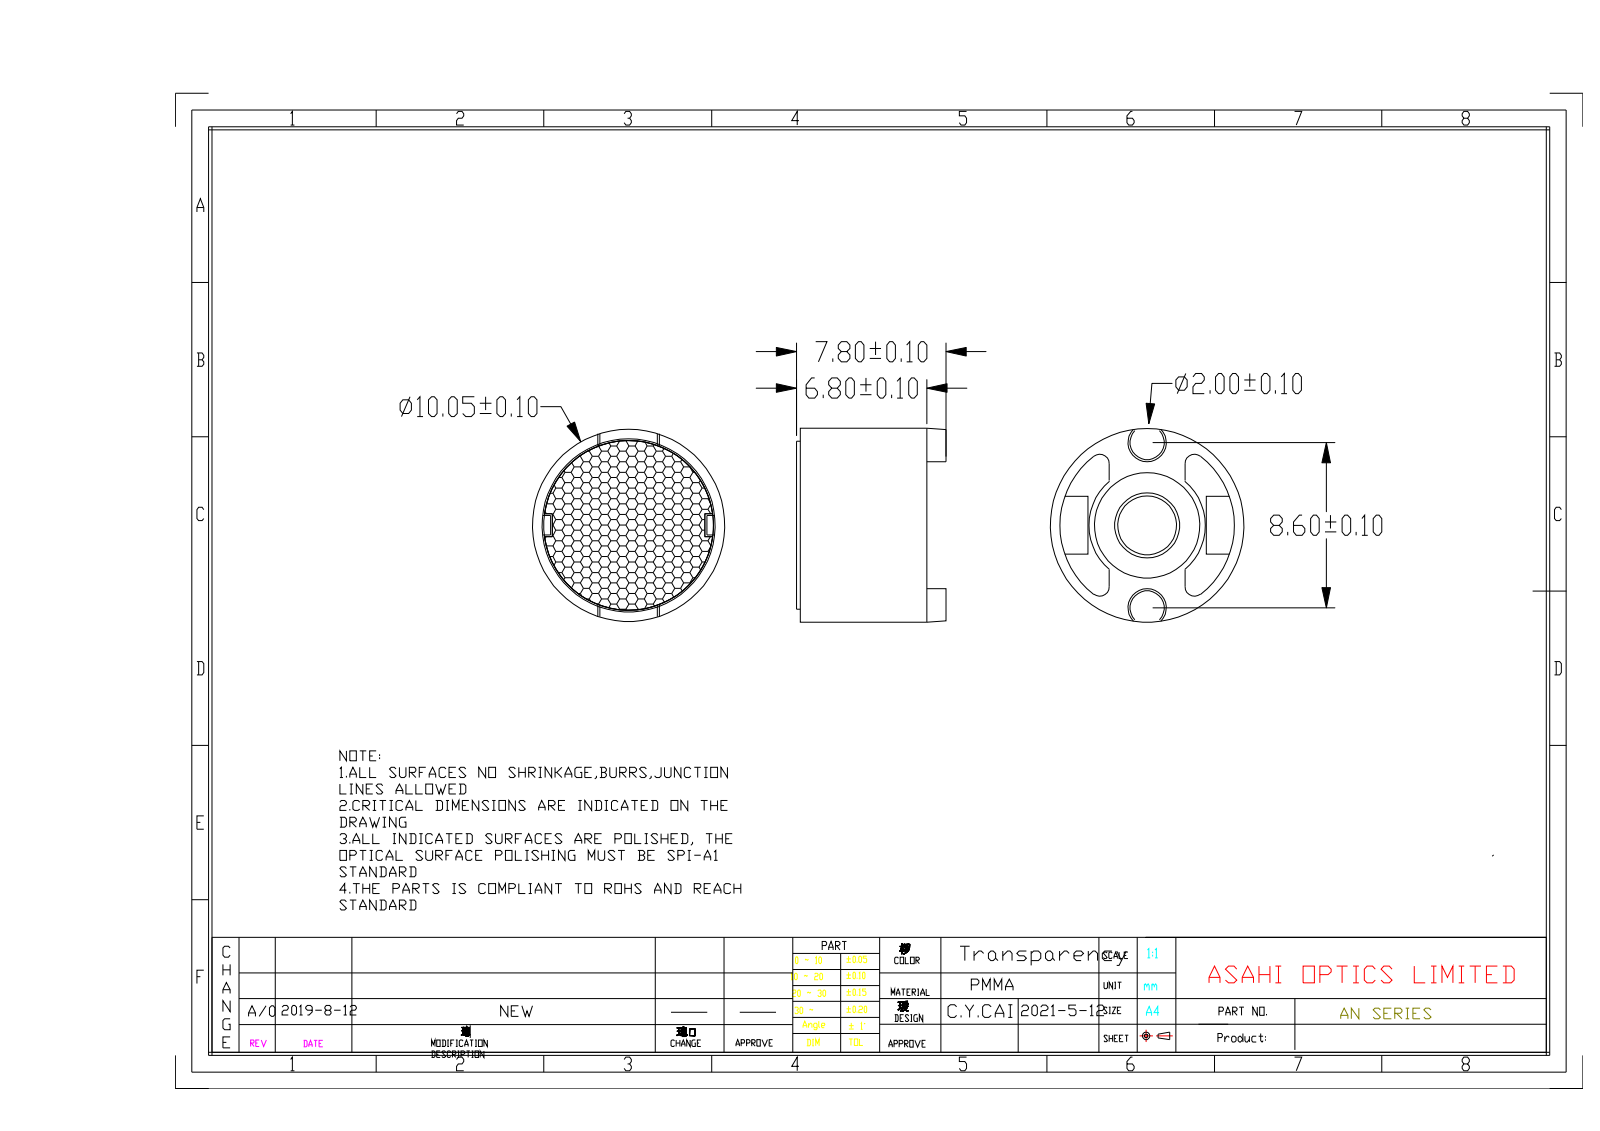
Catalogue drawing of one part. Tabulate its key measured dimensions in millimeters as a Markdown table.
| quantity | value |
| --- | --- |
| part name | AXXL; D10-A15L; ASM0001-D10_ASM |
| STEP written by | CREO PARAMETRIC BY PTC INC, 2018020 (CONFIG_CONTROL_DESIGN) |
| units | millimeters |
| bodies | 2 solids, 113 faces (66 planar, 9 cylindrical, 38 other) |
| overall size | 10.6 × 10.56 × 7.45 |
| volume | 379 mm³ |
| surface area | 755 mm² |
| partial cylindrical surfaces (radius × count) | 0.2 × 2, 0.3 × 2, 0.5 × 2, 0.5 × 2, 4.56 × 1 |
| main face-to-face distances | 6.38, 1.15, 5.23, 4.49, 3.1, 1.95, 3.28, 1.6, 0.55, 0.6 |
